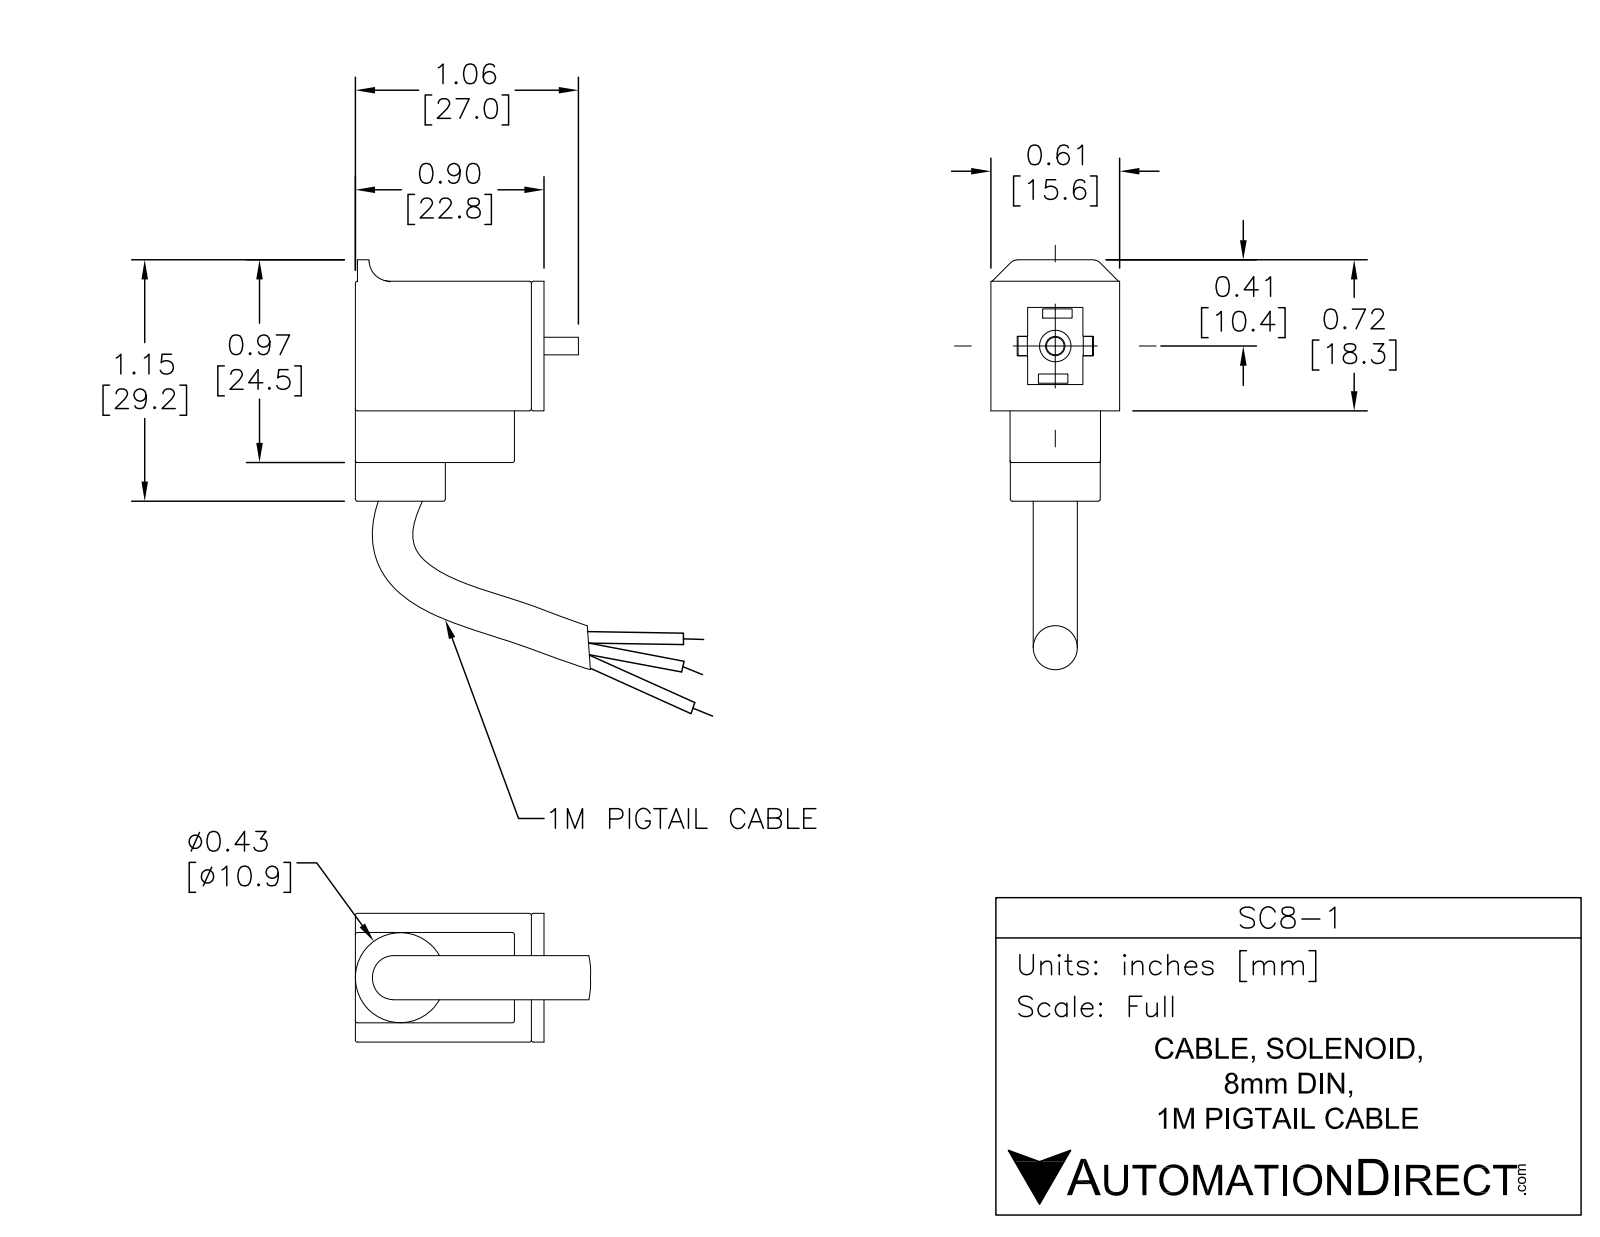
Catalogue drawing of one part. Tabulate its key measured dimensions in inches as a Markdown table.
| quantity | value |
| --- | --- |
| part name | SC8-1 |
| STEP written by | SolidWorks 2013 (AUTOMOTIVE_DESIGN) |
| units | inches |
| bodies | 1 solid, 143 faces (76 planar, 43 cylindrical, 24 other) |
| overall size | 1.951 × 1.119 × 0.613 |
| volume | 0.472 in³ |
| surface area | 5.856 in² |
| round holes (diameter × count) | 0.092 × 1, 0.15 × 1, 0.2 × 1 |
| round bosses / shafts (diameter × count) | 0.428 × 1, 0.193 × 1, 0.084 × 1 |
| partial cylindrical surfaces (radius × count) | 0.01 × 24, 0.05 × 2, 0.1 × 1 |
| main face-to-face distances | 0.613, 0.091, 0.522, 0.898, 0.1, 0.798, 0.617, 0.43, 0.246, 0.863 |
